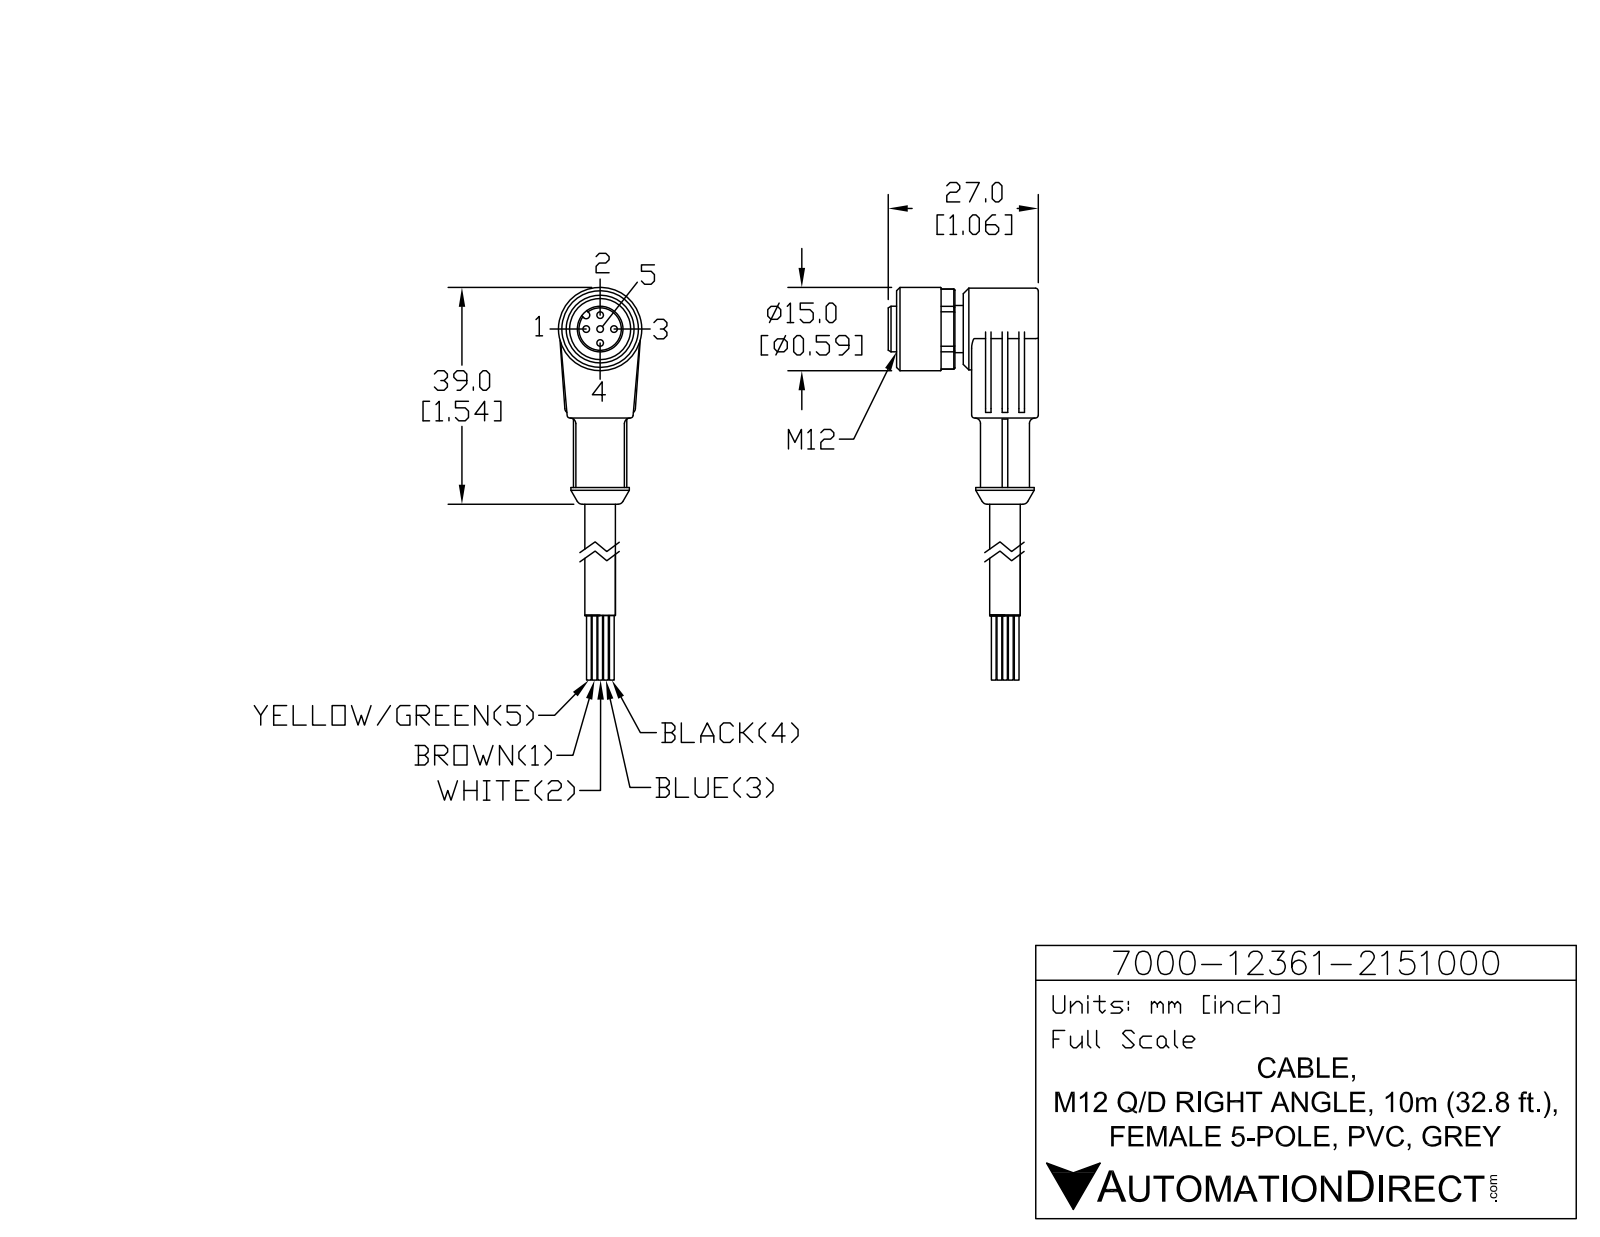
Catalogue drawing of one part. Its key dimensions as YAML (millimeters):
part_name: "7000-12361-2151000"
step_written_by: "SolidWorks 2015 (AUTOMOTIVE_DESIGN)"
units: millimeters
bodies: {solids: 1, faces: 150, planar: 61, cylindrical: 60, other: 29}
overall_size: [59, 27, 15]
volume: 6805
surface_area: 3613
round_holes:
  - {diameter: 1.2, count: 5}
  - {diameter: 4.8, count: 1}
  - {diameter: 11, count: 1}
round_bosses_or_shafts:
  - {diameter: 15, count: 1}
  - {diameter: 14.7, count: 1}
  - {diameter: 10.5, count: 1}
  - {diameter: 8.8, count: 1}
  - {diameter: 8.5, count: 1}
  - {diameter: 8.2, count: 1}
  - {diameter: 5.5, count: 1}
partial_cylinders:
  - {radius: 0.5, count: 8}
  - {radius: 1, count: 2}
  - {radius: 0.65, count: 1}
  - {radius: 7.2, count: 1}
face_to_face_distances: [12, 1.5, 3, 13.5, 15, 5.5, 9.5, 6, 8, 12.5]
hole_center_spacings: [2.5, 3.54, 5]
